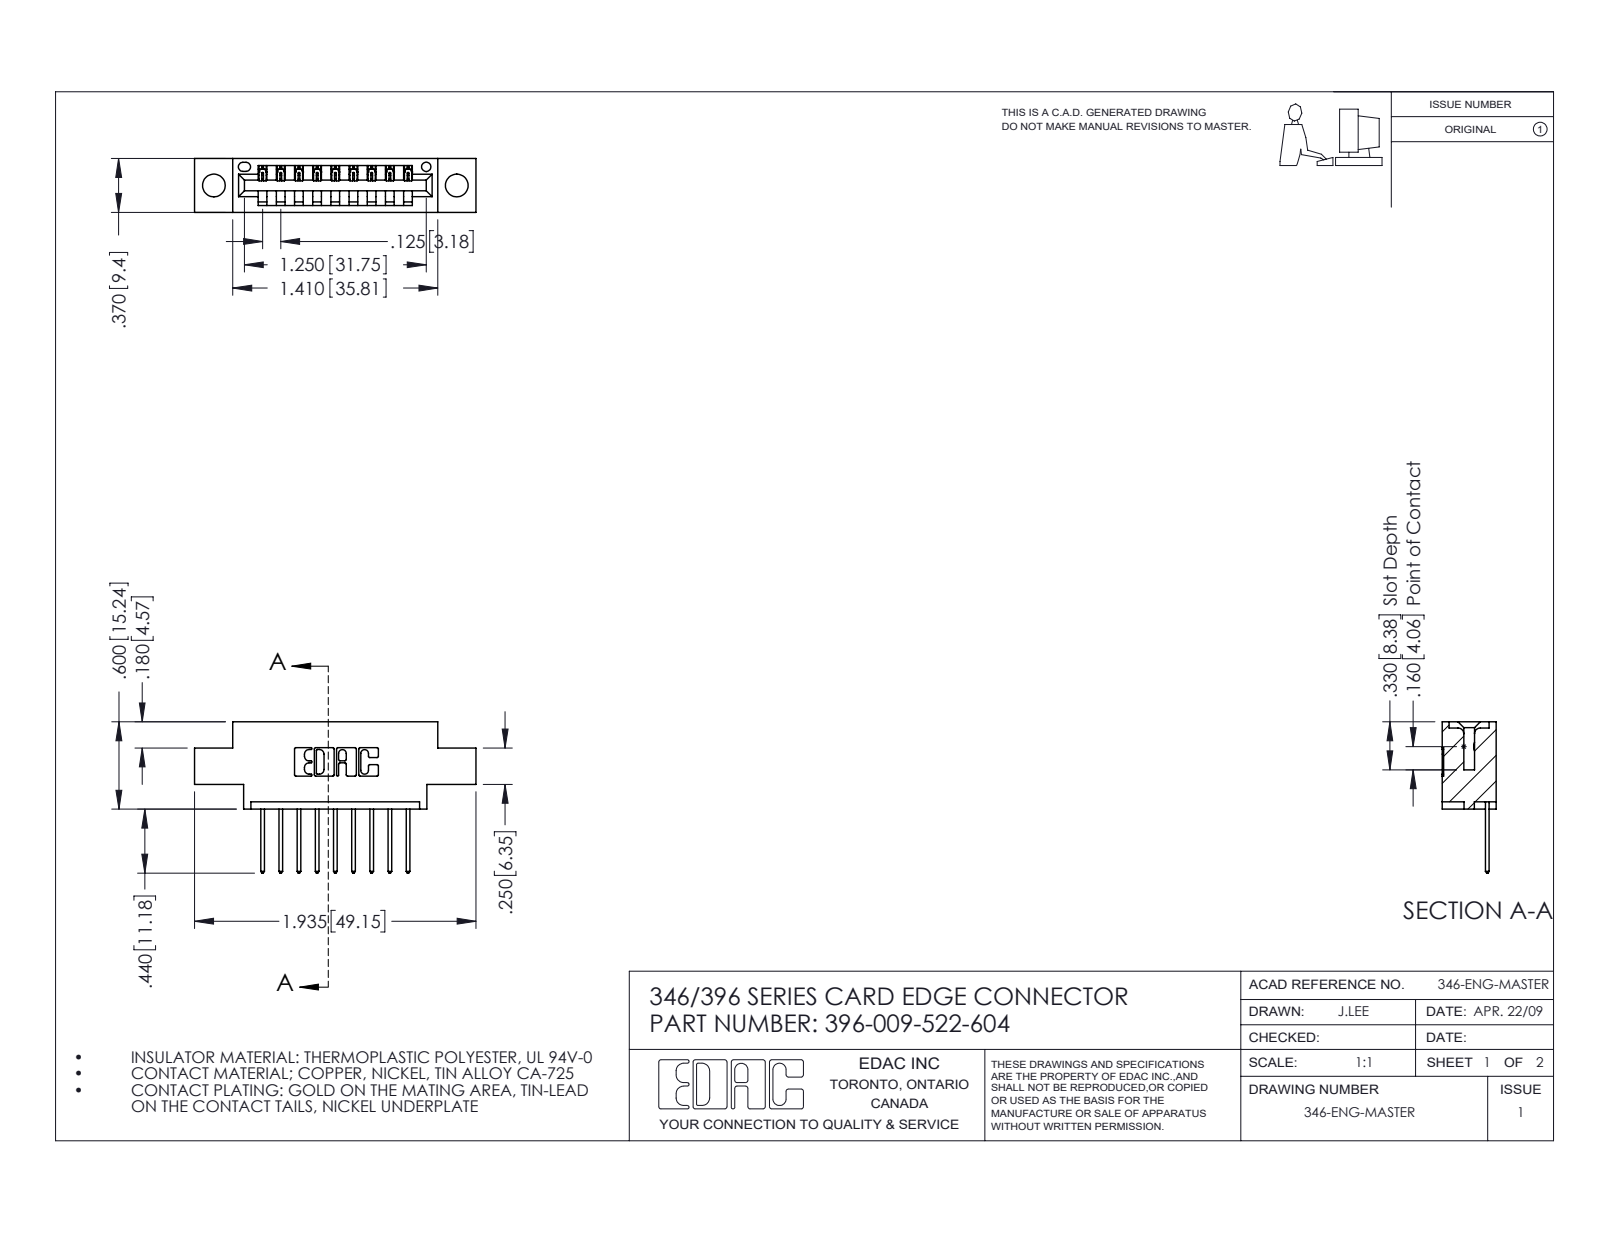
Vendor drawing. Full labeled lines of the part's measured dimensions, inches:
Part name (STEP PRODUCT): 346 Part_0.170 Offset - 0.156 Dia-TH; 396-009-522-604; 345-292-001_345-293-122
STEP written by: SolidWorks 2016 (CONFIG_CONTROL_DESIGN)
Units: inches
Bodies: 10 solids, 648 faces (440 planar, 208 cylindrical, 0 other)
Overall size (bounding box): 1.935 × 1.04 × 0.37
Volume: 0.258 in³ · Surface area: 7.652 in²
Round holes (diameter × count): ⌀0.156 ×2, ⌀0.064 ×1
Partial cylindrical surfaces — rounded edges, fillets, slot ends (radius × count): R0.01 ×22, R0.006 ×18, R0.01 ×18, R0.007 ×6, R0.031 ×6, R0.026 ×3, R0.031 ×2, R0.04 ×2
Main face-to-face distances: 0.25, 0.37, 0.048, 0.322, 0.072, 0.298, 0.025, 0.148, 0.222, 0.1
Hole centre spacings: 0.246, 1.465, 1.67
